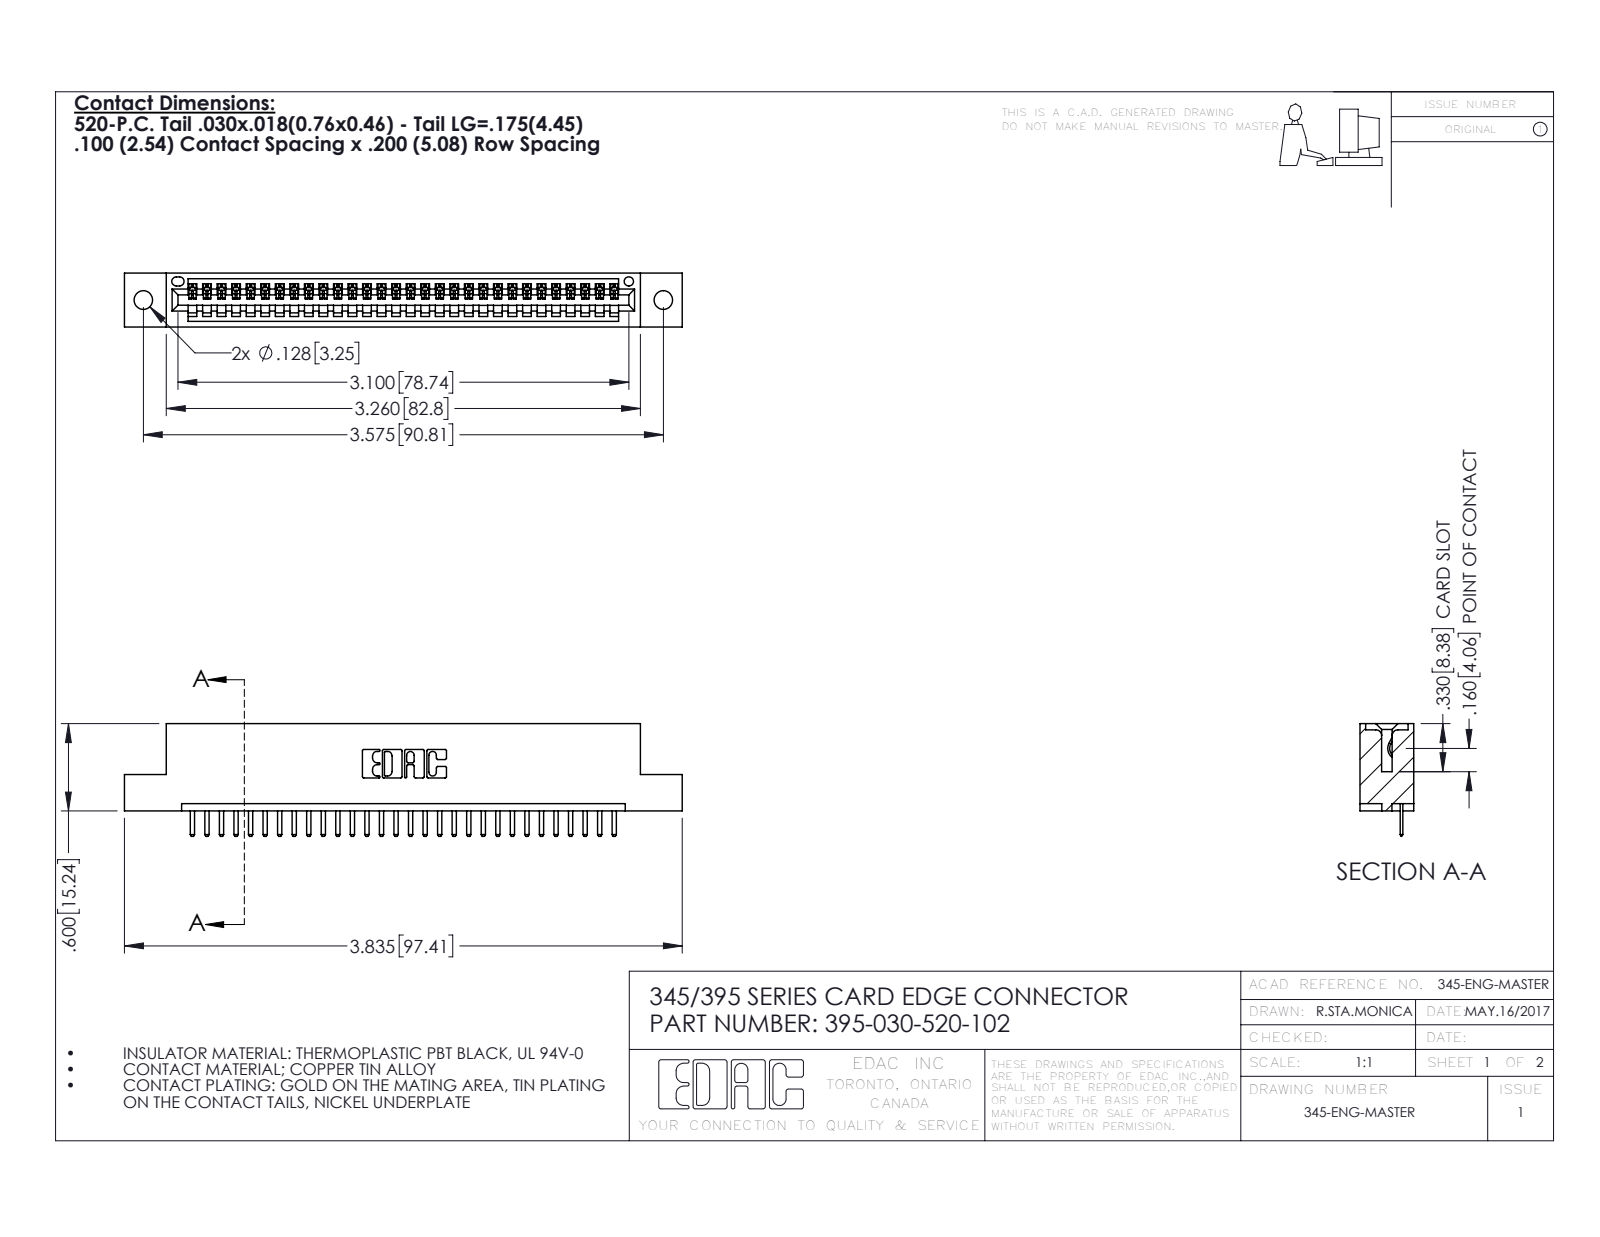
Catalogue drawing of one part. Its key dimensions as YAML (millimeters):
part_name: "395-030-520-102; 345-292-001_345-293-120; 345 Part_Flush Mounting Lugs - 0.128 Dia"
step_written_by: "SolidWorks 2016 (CONFIG_CONTROL_DESIGN)"
units: millimeters
bodies: {solids: 31, faces: 1986, planar: 1340, cylindrical: 646, other: 0}
overall_size: [97.4, 19.7, 9.4]
volume: 9030
surface_area: 11280
round_holes:
  - {diameter: 3.3, count: 2}
  - {diameter: 1.6, count: 1}
partial_cylinders:
  - {radius: 0.3, count: 62}
  - {radius: 0.2, count: 60}
  - {radius: 0.3, count: 22}
  - {radius: 0.2, count: 6}
  - {radius: 0.8, count: 6}
  - {radius: 0.7, count: 3}
  - {radius: 0.8, count: 2}
  - {radius: 1, count: 2}
face_to_face_distances: [7.6, 1.8, 9.4, 5.1, 2.5, 6.9, 0.6, 5.7, 1.8, 3.8]
hole_center_spacings: [6.9, 84.8, 90.8]
